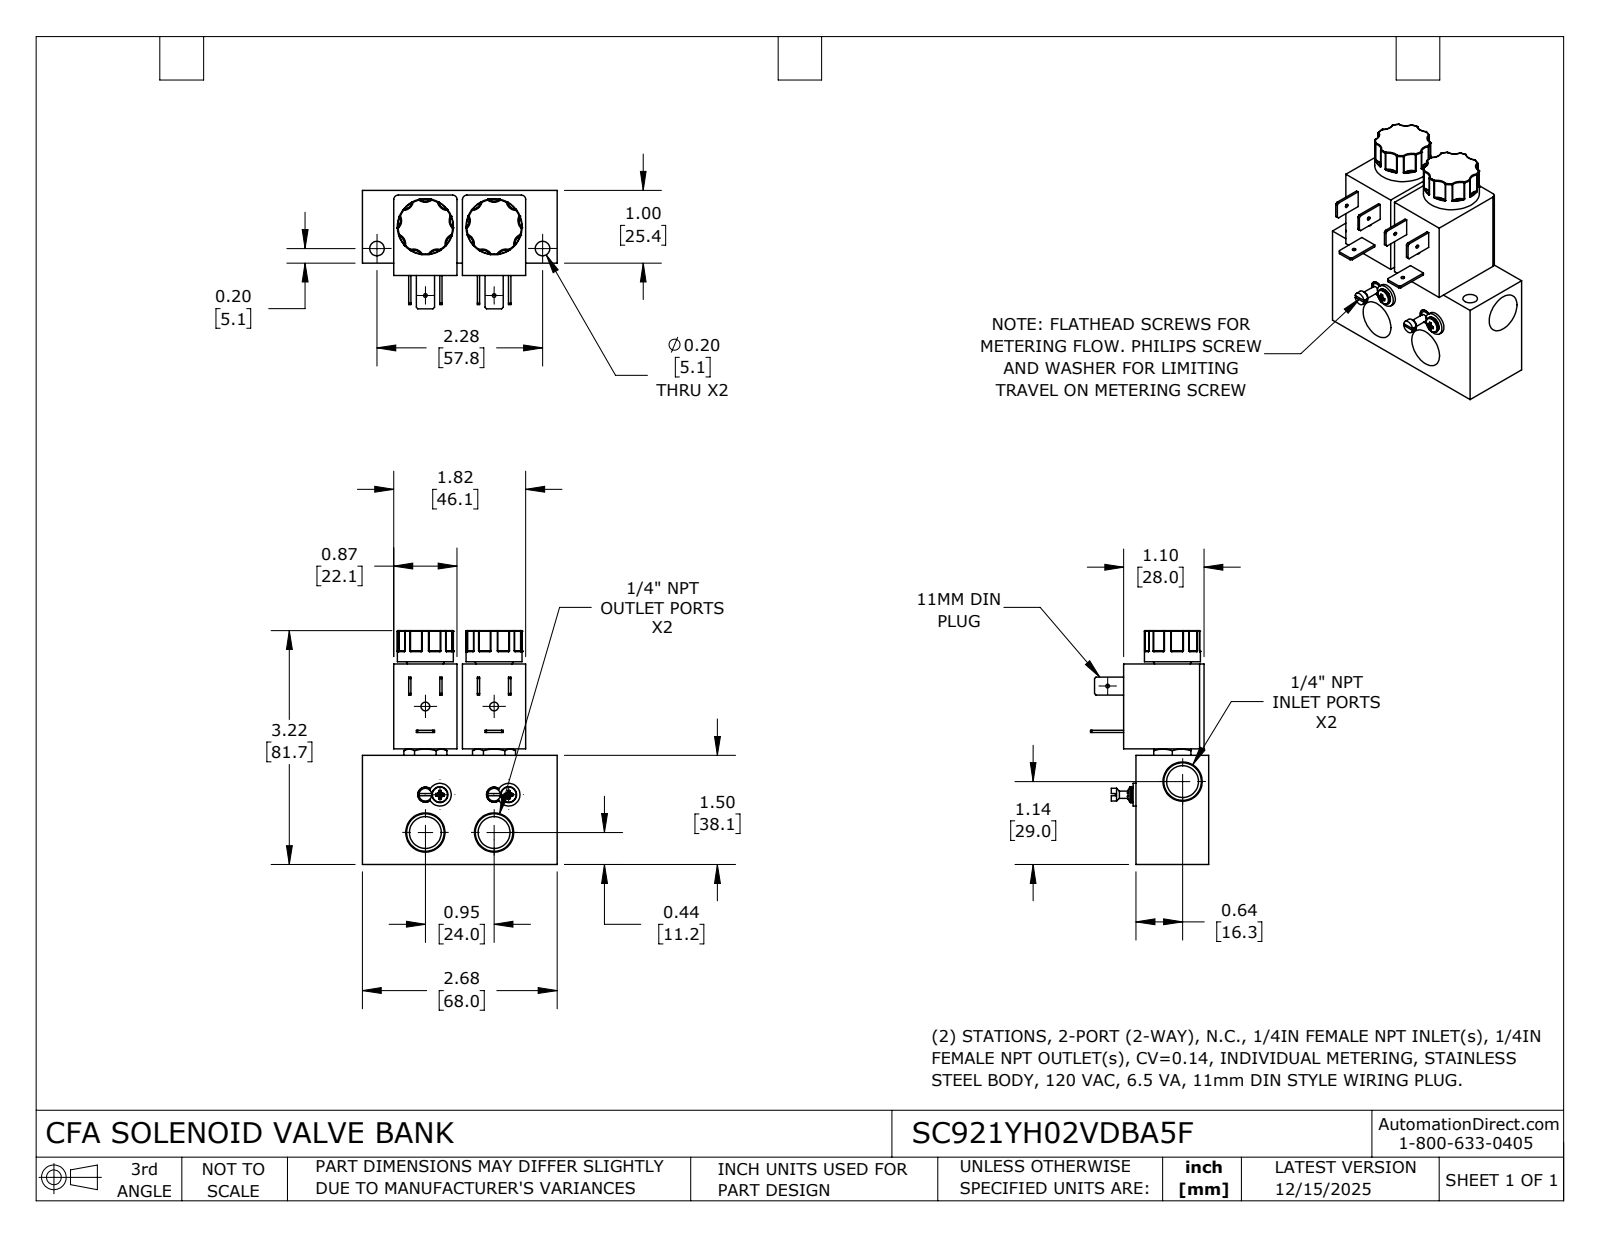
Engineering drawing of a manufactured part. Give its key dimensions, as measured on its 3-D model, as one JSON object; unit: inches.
{"part_name": "SC921YH02VDBA5F", "step_written_by": "SolidWorks 2024 (CONFIG_CONTROL_DESIGN)", "units": "inches", "bodies": {"solids": 1, "faces": 589, "planar": 156, "cylindrical": 152, "other": 281}, "overall_size": [3.215, 2.677, 1.627], "volume_in3": 6.159, "surface_area_in2": 40.27, "round_holes": [[0.05, 3], [0.438, 3], [0.12, 2], [0.2, 2], [0.208, 2]], "round_bosses_or_shafts": [[0.77, 2], [0.312, 2], [0.219, 2], [0.206, 2], [0.175, 2], [0.102, 2], [0.1, 2]], "partial_cylinders_radius": [[0.01, 36], [0.133, 18], [0.06, 4], [0.308, 1]], "face_to_face_distances": [1, 0.945, 0.431, 1.301, 1.376, 2.246, 0.87, 1.5, 1.169, 0.169], "hole_center_spacings": [0.945, 0.52, 0.928, 1.078, 1.212, 1.537, 1.732, 1.735]}
